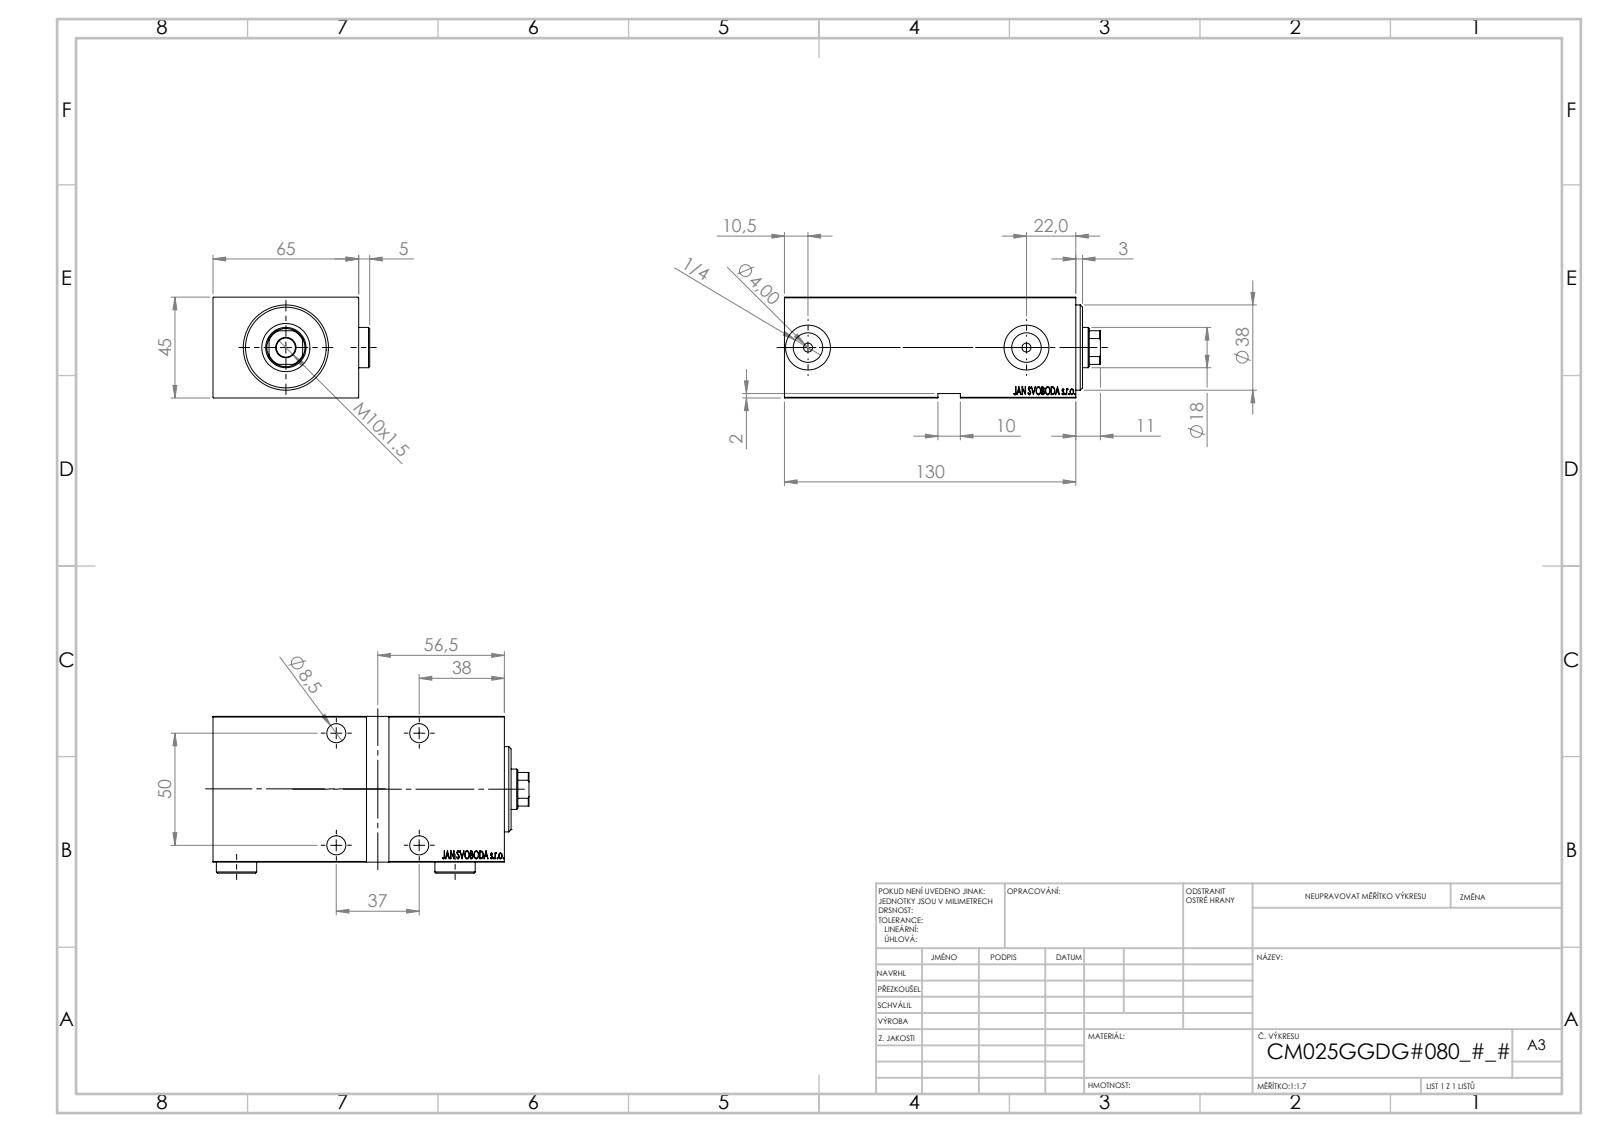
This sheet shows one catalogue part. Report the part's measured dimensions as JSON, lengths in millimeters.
{"part_name": "V450CM_G_VCP; V450CM_G_Body; Zatka_OIL_PORT; V450CM_VC_G", "step_written_by": "SolidWorks 2019 (CONFIG_CONTROL_DESIGN)", "units": "millimeters", "bodies": {"solids": 5, "faces": 913, "planar": 445, "cylindrical": 70, "other": 398}, "overall_size": [141, 69.9, 45], "volume_mm3": 344529, "surface_area_mm2": 67400, "round_holes": [[8.5, 5], [13.5, 4], [4, 2], [13.16, 2], [20, 2], [18, 1], [21.5, 1], [25, 1], [27, 1], [35, 1]], "round_bosses_or_shafts": [[18, 2], [38, 1]], "partial_cylinders_radius": [[8.5, 1]], "face_to_face_distances": [45, 65, 130, 6, 64.9, 119, 5, 124, 8, 125], "hole_center_spacings": [37, 50, 62.2, 97.5]}
